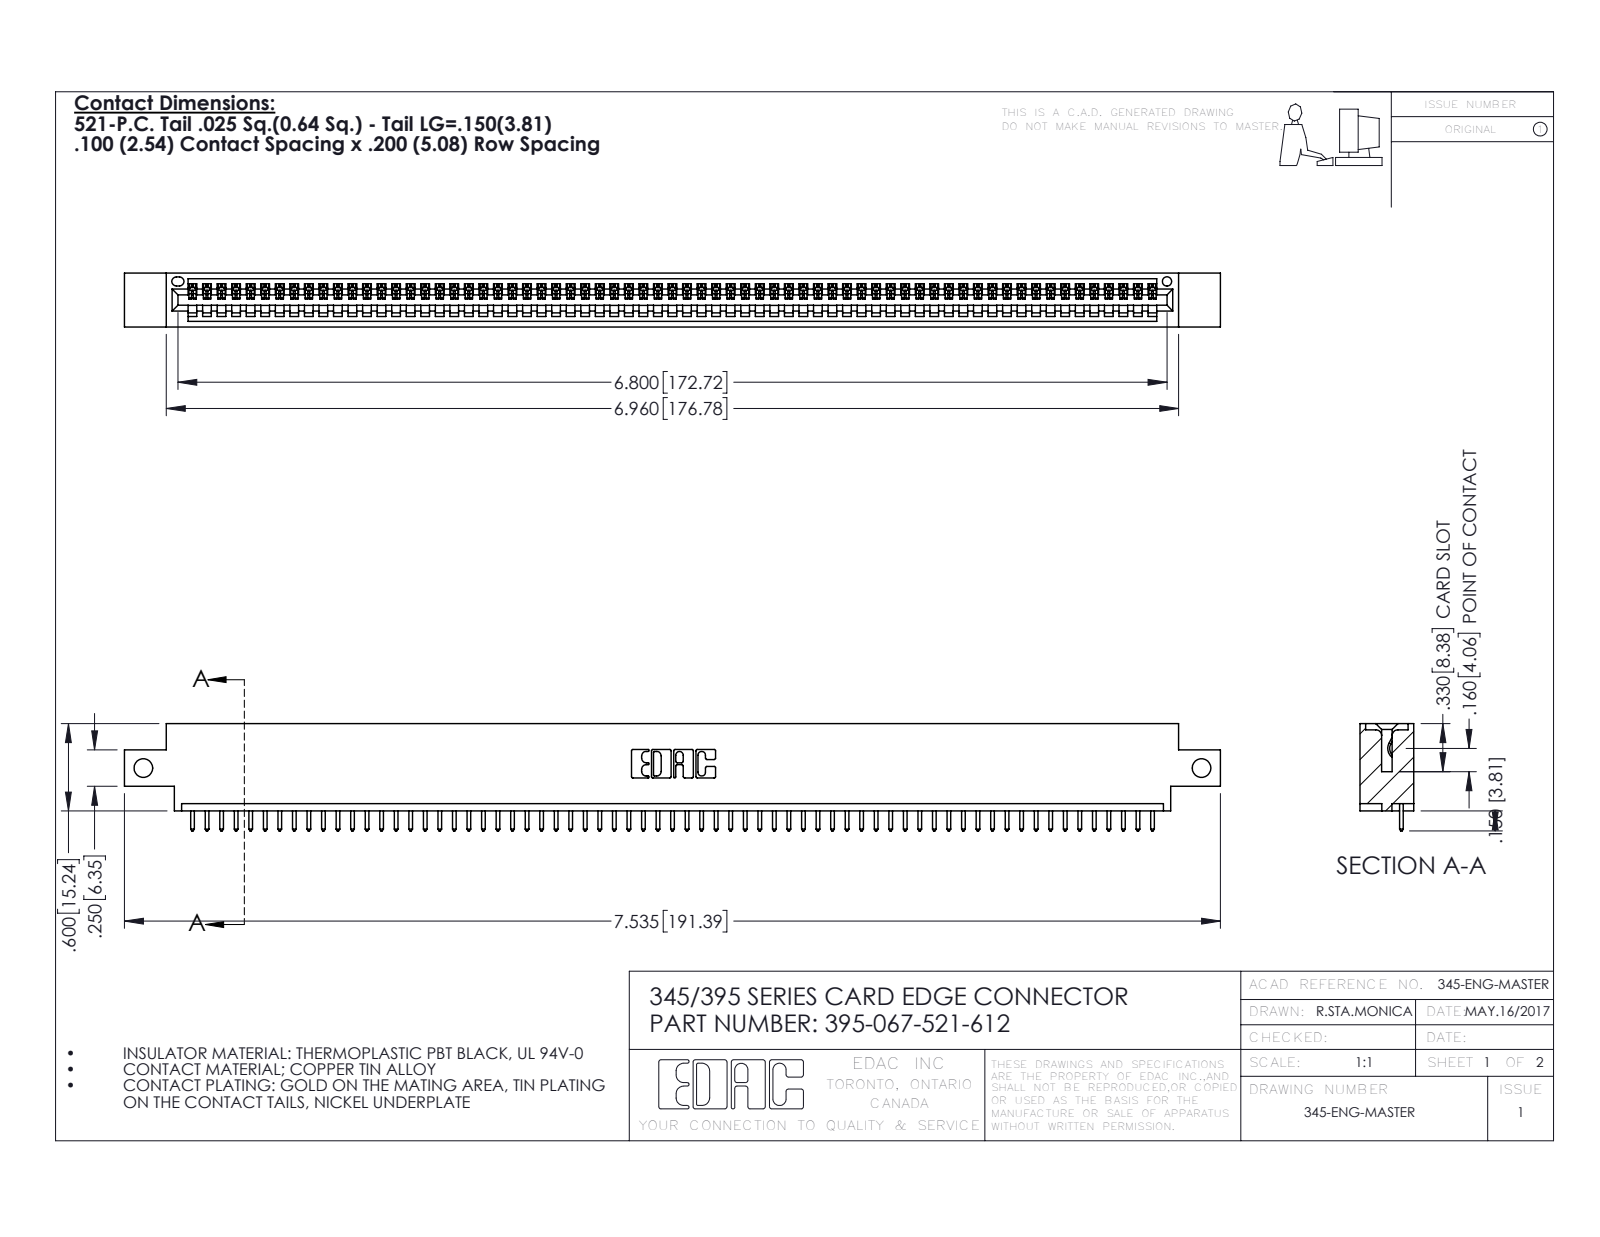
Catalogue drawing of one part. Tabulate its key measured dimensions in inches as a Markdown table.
| quantity | value |
| --- | --- |
| part name | 345 Part_0.170 Offset - Side Mount; 345-292-001_345-293-121; 395-067-521-612 |
| STEP written by | SolidWorks 2016 (CONFIG_CONTROL_DESIGN) |
| units | inches |
| bodies | 68 solids, 4016 faces (2764 planar, 1252 cylindrical, 0 other) |
| overall size | 7.535 × 0.737 × 0.37 |
| volume | 1.098 in³ |
| surface area | 36.41 in² |
| round holes (diameter × count) | 0.128 × 2, 0.064 × 1 |
| partial cylindrical surfaces (radius × count) | 0.006 × 134, 0.01 × 134, 0.01 × 22, 0.007 × 6, 0.031 × 6, 0.026 × 3, 0.031 × 2, 0.04 × 2 |
| main face-to-face distances | 0.298, 0.072, 0.37, 0.2, 0.098, 0.272, 0.025, 0.225, 0.175, 0.149 |
| hole center spacings | 7.275 |
